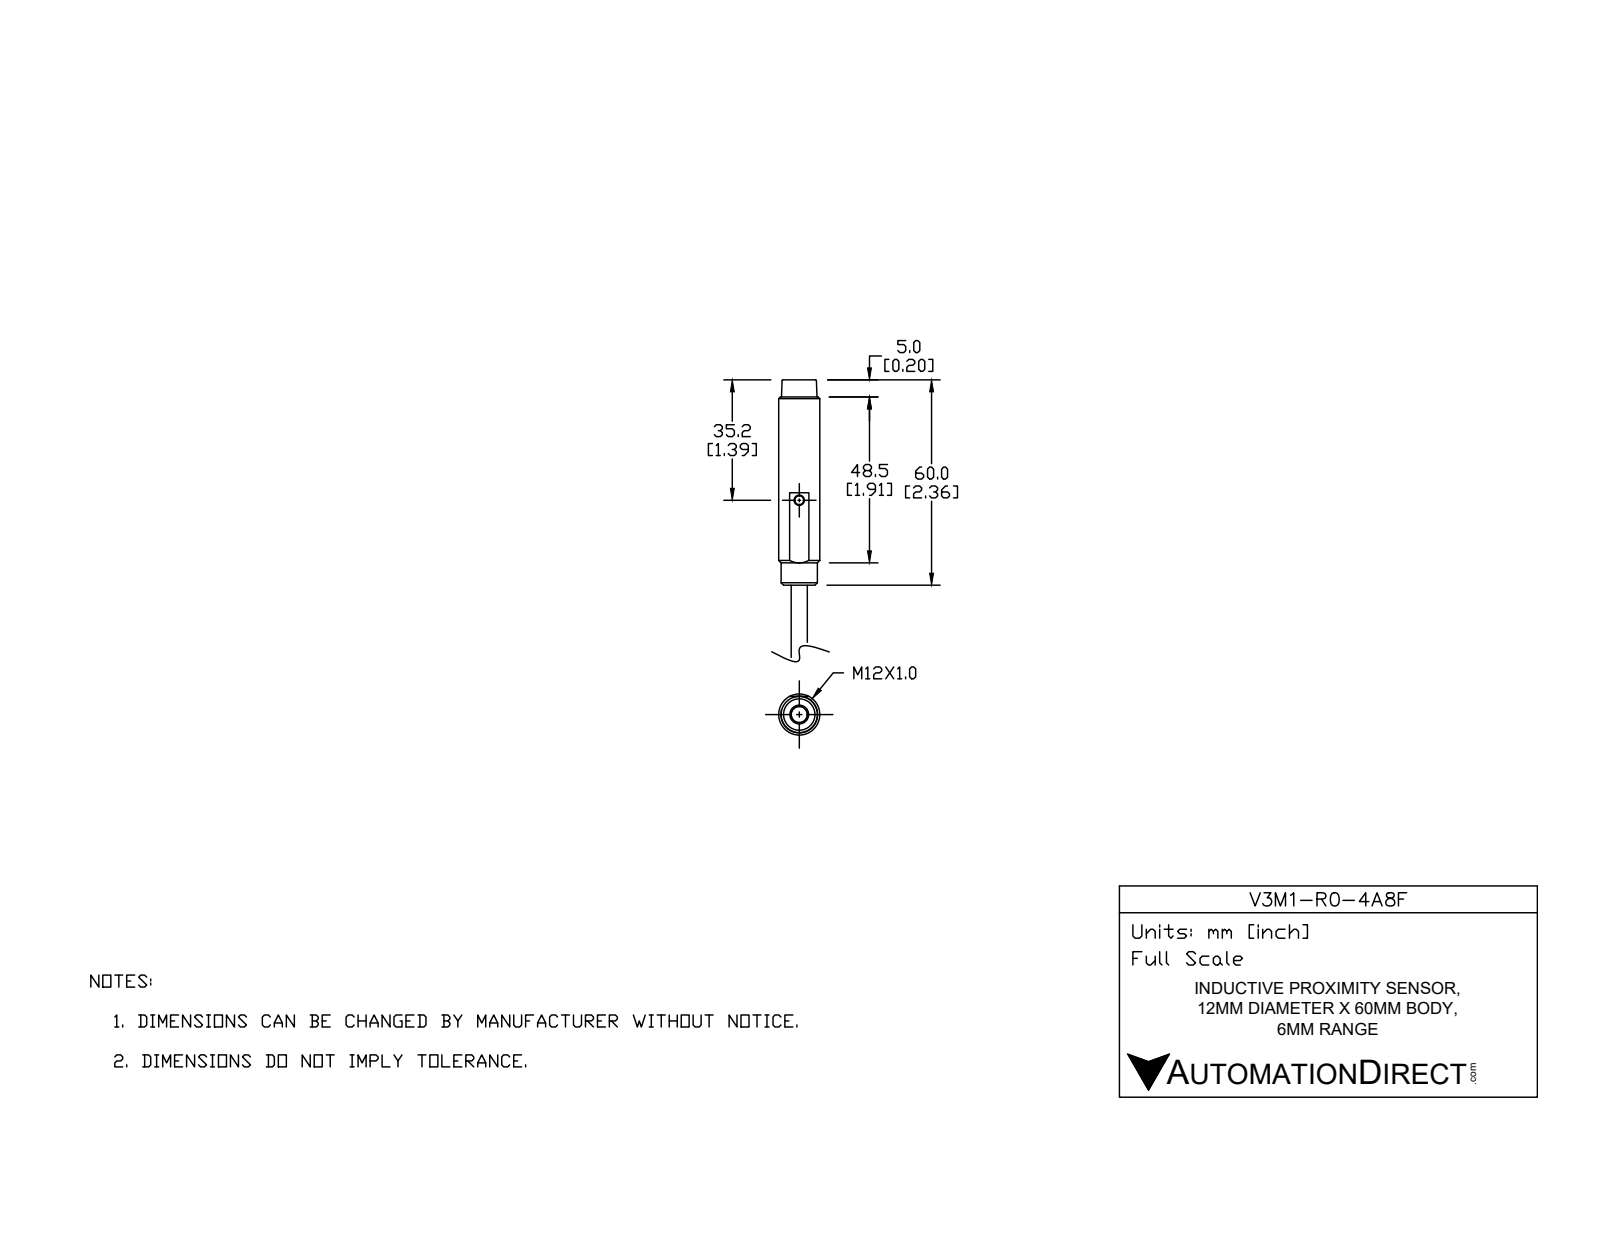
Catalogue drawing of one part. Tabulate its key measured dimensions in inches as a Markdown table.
| quantity | value |
| --- | --- |
| part name | V3M1_4A_fig |
| STEP written by | ST-DEVELOPER v16.7 (AUTOMOTIVE_DESIGN) |
| units | inches |
| bodies | 1 solid, 19 faces (8 planar, 4 cylindrical, 7 other) |
| overall size | 3.898 × 0.472 × 0.472 |
| volume | 0.431 in³ |
| surface area | 4.633 in² |
| round holes (diameter × count) | 0.102 × 1 |
| round bosses / shafts (diameter × count) | 0.472 × 1, 0.417 × 1, 0.185 × 1 |
| main face-to-face distances | 2.362, 3.898, 1.535, 0.197, 2.165, 3.701, 0.051, 1.299, 1.102, 1.063 |
